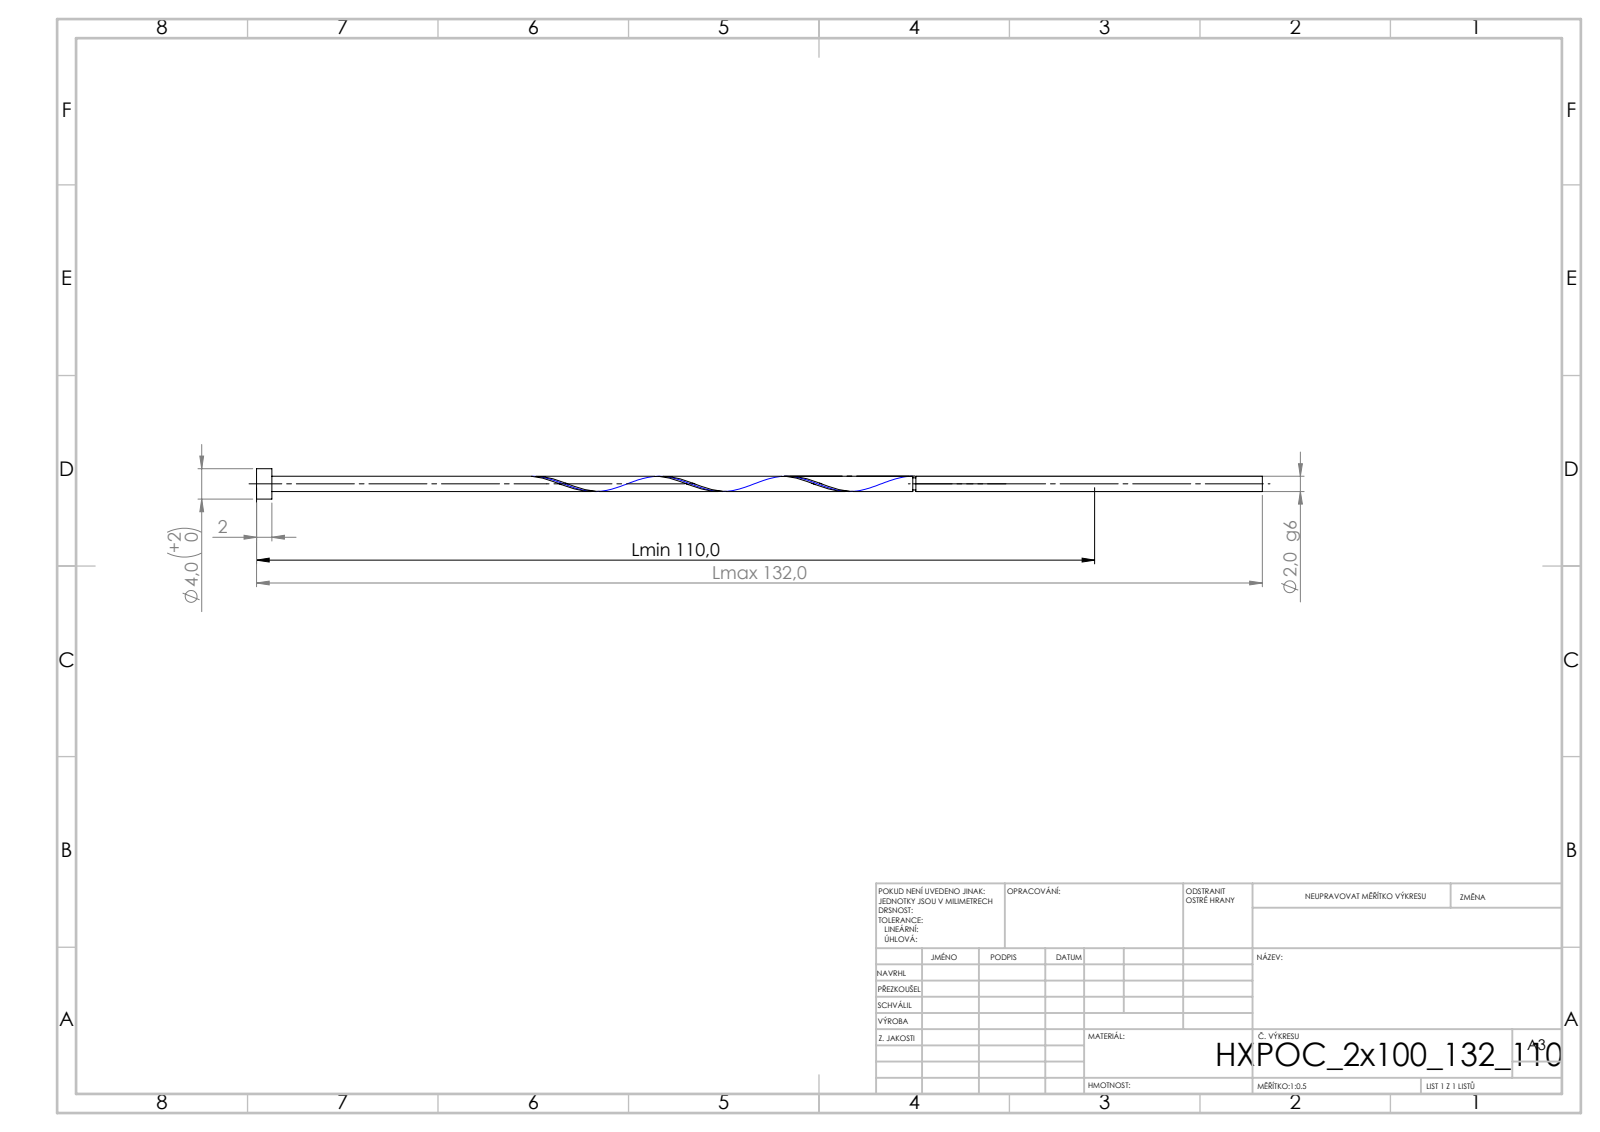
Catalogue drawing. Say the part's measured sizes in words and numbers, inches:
Its 3-D file was written by "SolidWorks 2019 (CONFIG_CONTROL_DESIGN)". It is 1 solid with 21 faces: 6 planar, 14 cylindrical and 1 other. Overall it measures 5.197 by 0.157 by 0.157 inches. Its volume is 0.026 cubic inches and its surface area 1.36 square inches. Round bosses or shafts: 1 of diameter 0.157, 1 of diameter 0.079, 1 of diameter 0.063. The main face-to-face distances are 0.079, 5.197, 5.118, 3.407, 3.328, 1.79, 3.391, 3.313, 0.016, 1.806.
